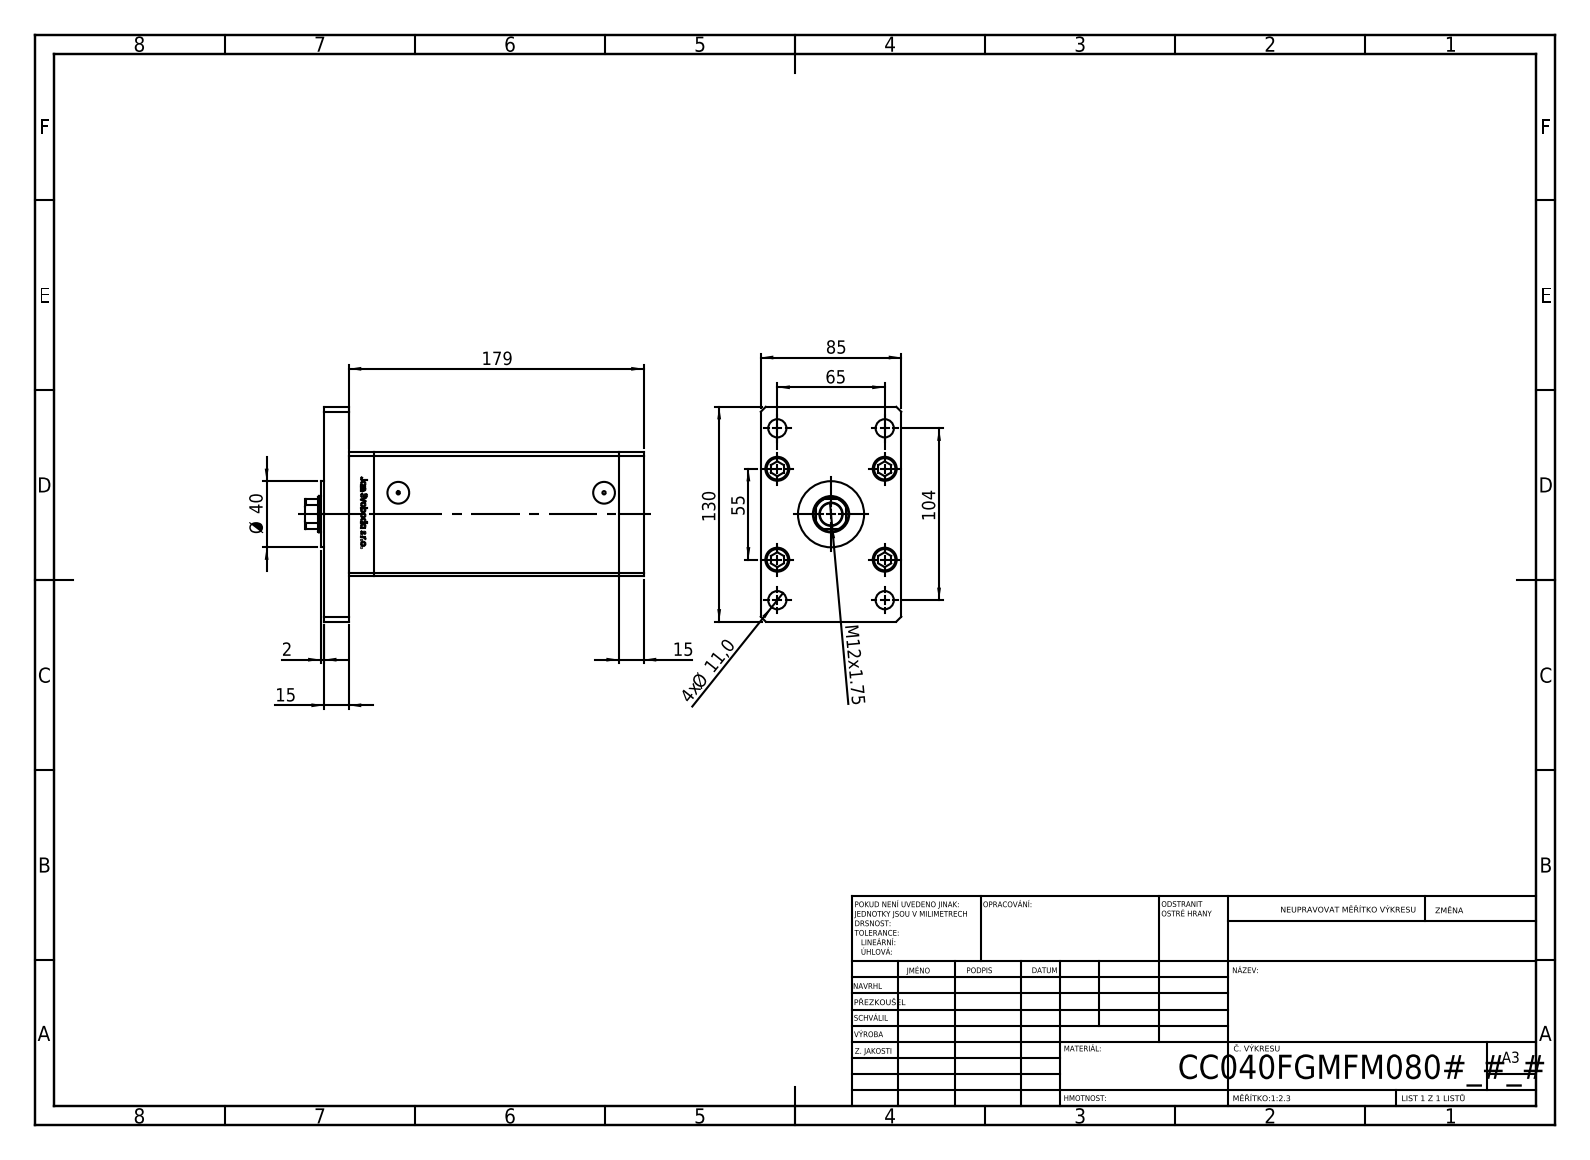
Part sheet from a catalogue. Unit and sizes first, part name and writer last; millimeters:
Units: millimetres
Overall size (bounding box): 205 × 130 × 85
Round holes (diameter × count): ⌀11 ×9, ⌀15.5 ×5, ⌀10 ×4, ⌀14.5 ×4, ⌀2 ×2, ⌀13.16 ×2, ⌀13.5 ×1, ⌀22 ×1, ⌀23.5 ×1
Round bosses / shafts (diameter × count): ⌀8 ×9, ⌀14.5 ×5, ⌀40 ×1
Partial cylindrical surfaces — rounded edges, fillets, slot ends (radius × count): R0.93 ×2, R10.5 ×1
Main face-to-face distances: 15, 85, 163.5, 178.5, 75, 148.5, 30, 193.5, 10.5, 27.5
Hole centre spacings: 28, 24.5, 42.57, 61.32, 65, 69.46, 79.5, 102.69
Volume: 1 165 000 mm³ · Surface area: 198 848 mm²
Bodies: 19 solids, 1308 faces (515 planar, 187 cylindrical, 606 other)
Part name (STEP PRODUCT): V220C BACK_F; V220C_VC_F; V220C_F; V220C_F_MIDDLE (+2 more)
STEP written by: SolidWorks 2019 (CONFIG_CONTROL_DESIGN)
